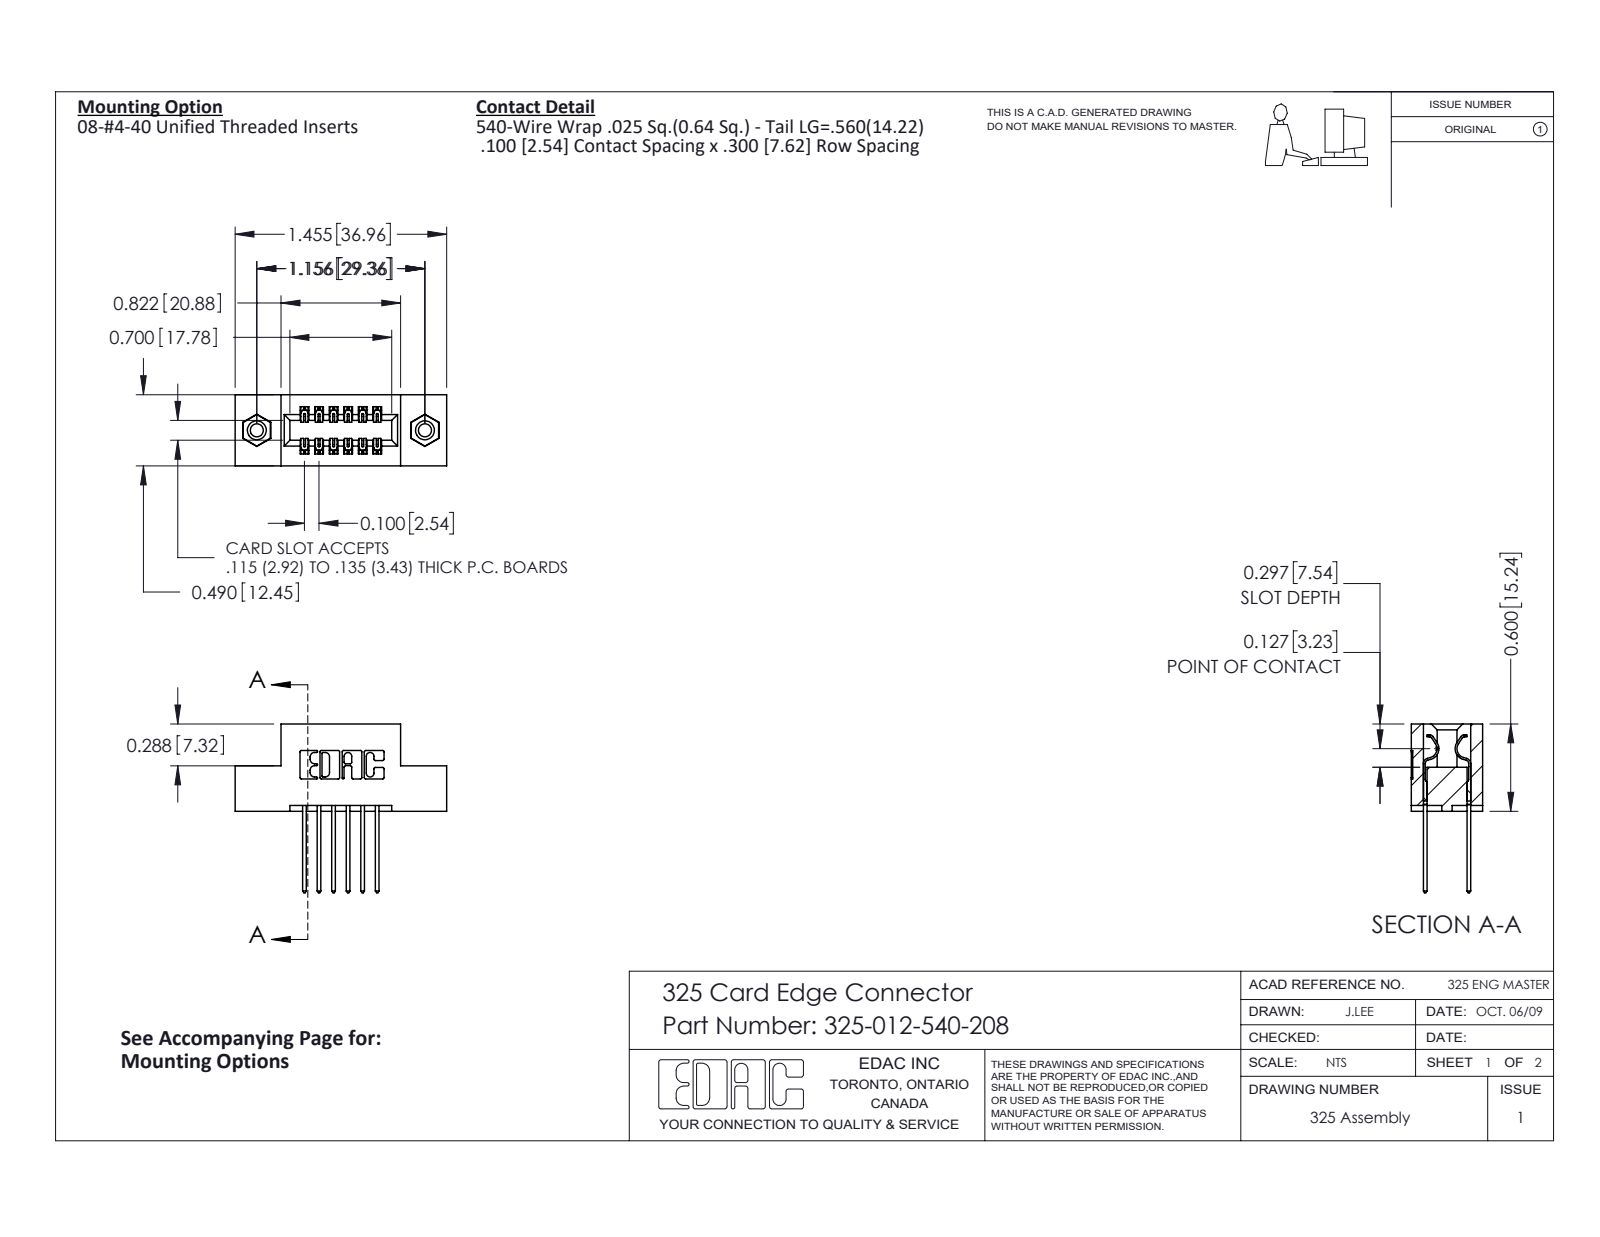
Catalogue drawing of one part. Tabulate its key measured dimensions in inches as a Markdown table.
| quantity | value |
| --- | --- |
| part name | 325-012-540-208; 325 Part_TI; 325-292-001_325-293-140; 345-250-001_345-250-003-102 |
| STEP written by | SolidWorks 2016 (CONFIG_CONTROL_DESIGN) |
| units | inches |
| bodies | 15 solids, 798 faces (534 planar, 248 cylindrical, 16 other) |
| overall size | 1.455 × 1.16 × 0.49 |
| volume | 0.274 in³ |
| surface area | 7.451 in² |
| round holes (diameter × count) | 0.089 × 2, 0.125 × 2, 0.16 × 2 |
| round bosses / shafts (diameter × count) | 0.155 × 2 |
| partial cylindrical surfaces (radius × count) | 0.01 × 22, 0.006 × 18, 0.01 × 12, 0.007 × 6, 0.031 × 6, 0.026 × 3, 0.014 × 2, 0.022 × 2 |
| main face-to-face distances | 0.3, 0.083, 0.407, 0.1, 0.49, 0.04, 0.2, 0.383, 0.107, 0.025 |
| hole center spacings | 1.156 |
